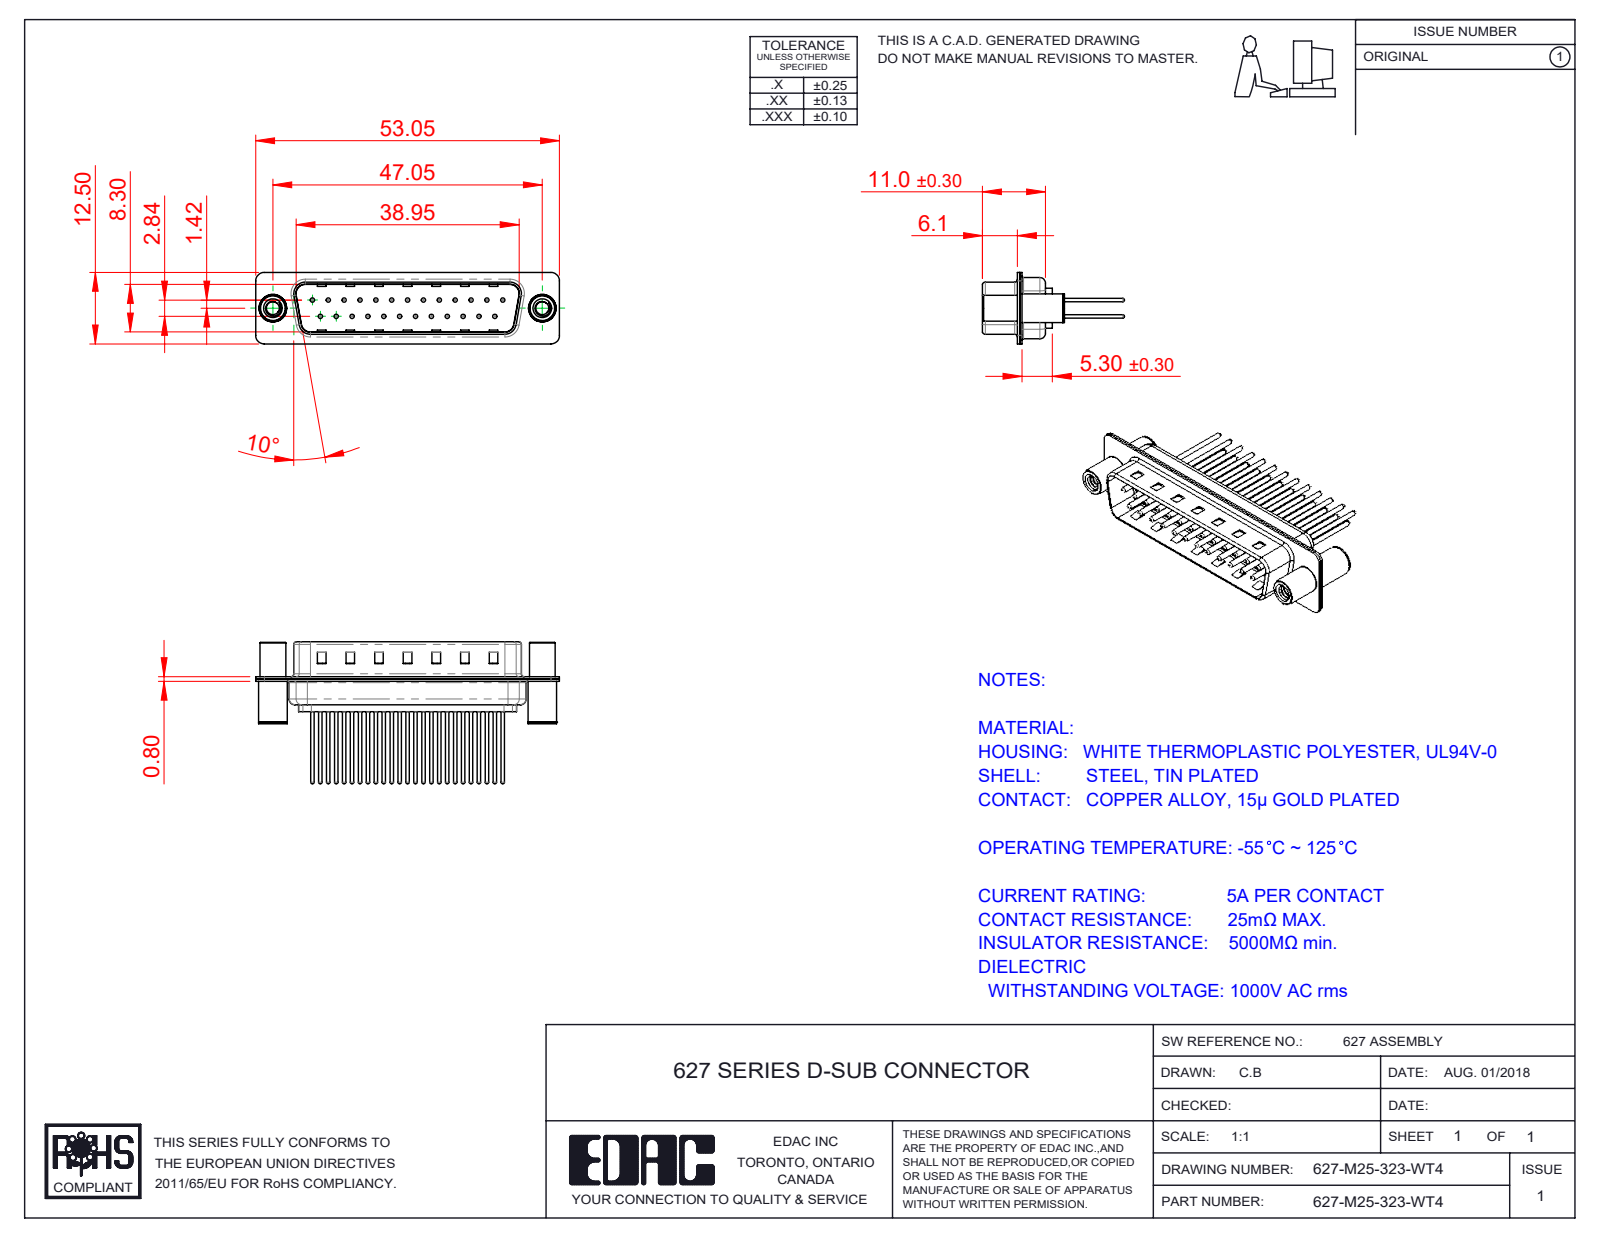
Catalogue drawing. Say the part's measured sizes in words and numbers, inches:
The part is named "627M Shell Front_25 Contacts; 627M Contact Row 1_23; 627M Contact Row 2_23; 627-M25-323-WT4 (+3 more)". Its 3-D file was written by "SolidWorks 2020 (CONFIG_CONTROL_DESIGN)". It is 30 solids with 1387 faces: 352 planar, 539 cylindrical and 496 other. Overall it measures 2.089 by 0.975 by 0.492 inches. Its volume is 0.186 cubic inches and its surface area 11.93 square inches. Round holes: 25 of diameter 0.03, 25 of diameter 0.063, 25 of diameter 0.079, 2 of diameter 0.089, 2 of diameter 0.128, 2 of diameter 0.157, 2 of diameter 0.189. Round bosses or shafts: 25 of diameter 0.059, 25 of diameter 0.024, 2 of diameter 0.197, 2 of diameter 0.193, 2 of diameter 0.177. Partial cylindrical surfaces (rounded edges, fillets, slot ends): 16 of radius 0.059, 12 of radius 0.079, 8 of radius 0.02, 8 of radius 0.063, 4 of radius 0.01, 4 of radius 0.024, 4 of radius 0.026, 4 of radius 0.035. The main face-to-face distances are 0.016, 0.031, 0.374, 0.358, 0.343, 0.39, 0.047, 0.224, 0.24, 0.03. The hole center spacings are 0.124, 0.109, 0.218, 0.327, 0.436, 0.545, 0.654, 0.198.
